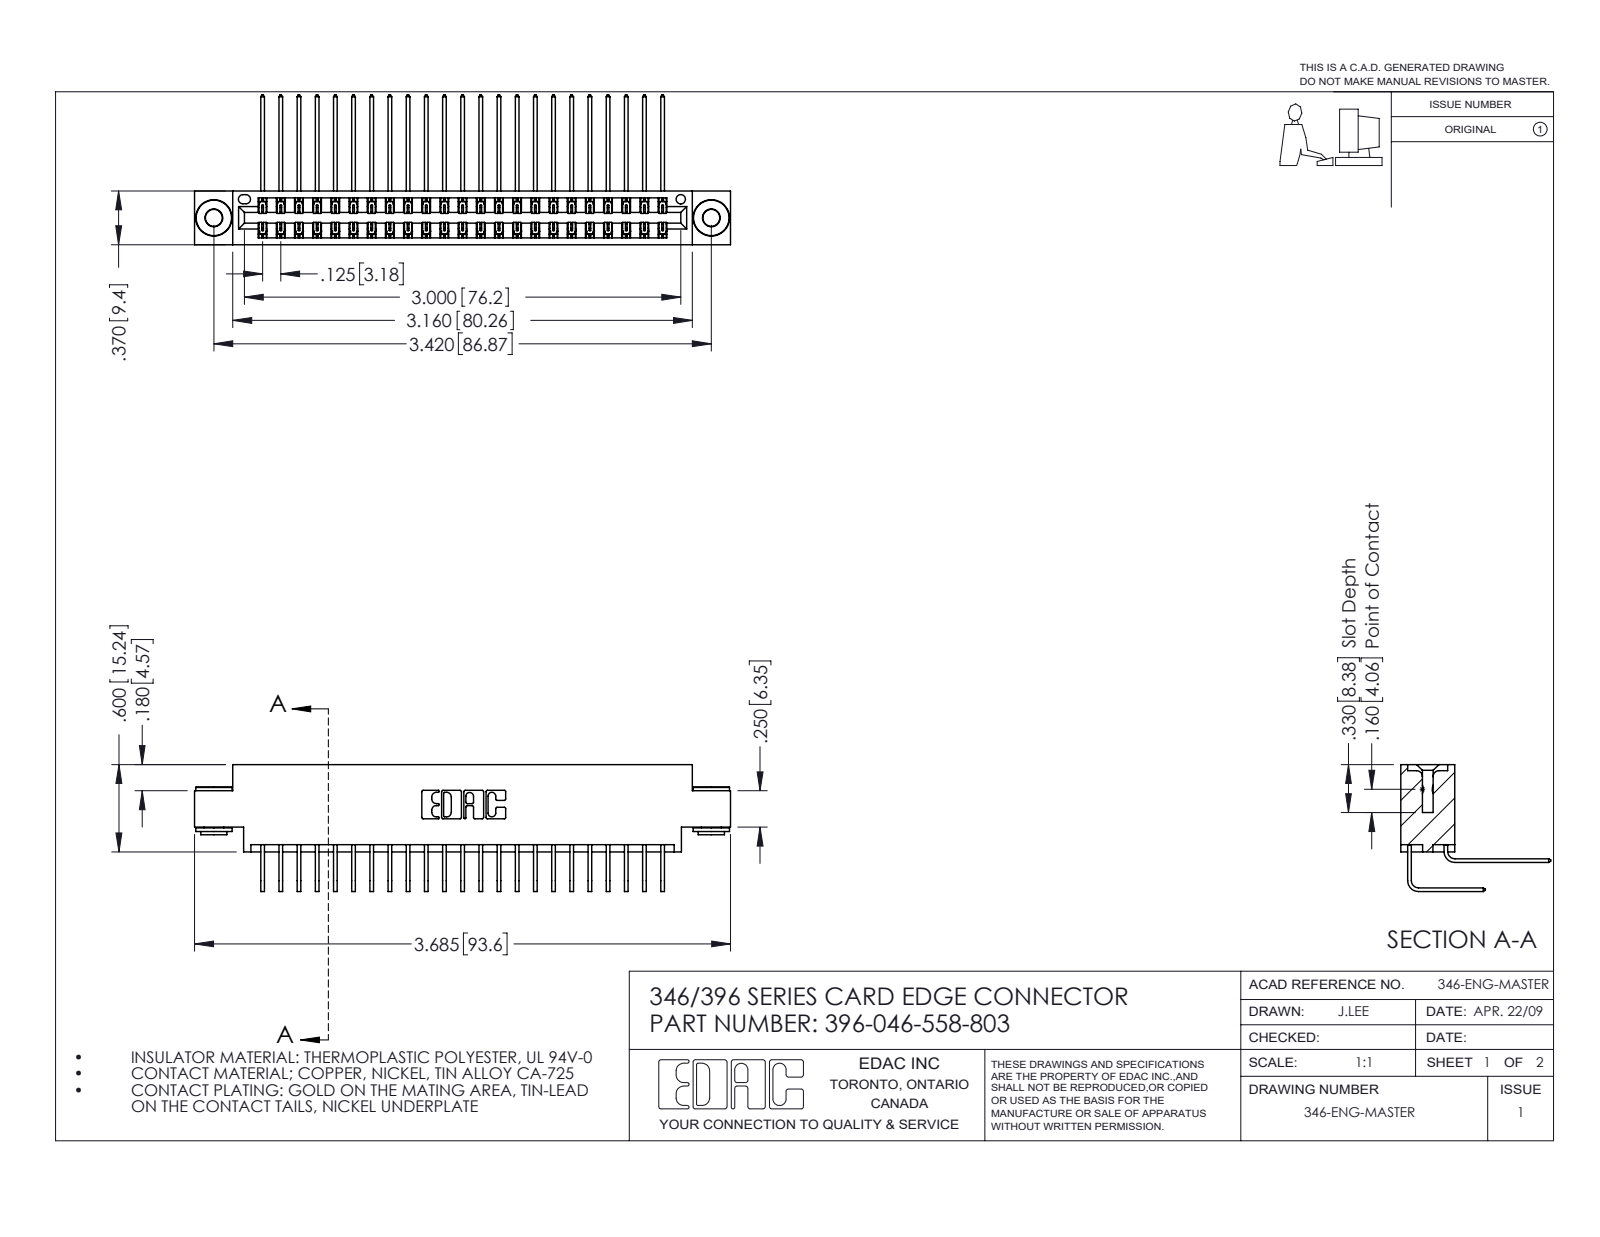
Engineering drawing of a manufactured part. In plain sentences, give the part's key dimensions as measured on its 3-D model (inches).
The part is named "396-046-558-803; 345-292-001_558 Tail - 2; 345-292-001_558 559 Tail - 1; 346 Part_0.170 Offset - 0.156 Dia-TH (+1 more)". Its 3-D file was written by "SolidWorks 2016 (CONFIG_CONTROL_DESIGN)". It is 49 solids with 2648 faces: 1792 planar, 848 cylindrical and 8 other. Overall it measures 3.685 by 1.03 by 0.873 inches. Its volume is 0.556 cubic inches and its surface area 21.53 square inches. Round holes: 2 of diameter 0.116, 2 of diameter 0.156, 1 of diameter 0.064. Round bosses or shafts: 2 of diameter 0.25, 2 of diameter 0.18, 2 of diameter 0.136. Partial cylindrical surfaces (rounded edges, fillets, slot ends): 69 of radius 0.006, 22 of radius 0.01, 6 of radius 0.007, 6 of radius 0.031, 3 of radius 0.026, 2 of radius 0.014, 2 of radius 0.022, 2 of radius 0.024. The main face-to-face distances are 0.322, 0.048, 0.025, 0.37, 0.25, 0.298, 0.072, 0.275, 0.148, 0.222. The hole center spacings are 0.246, 3.212, 3.42.
